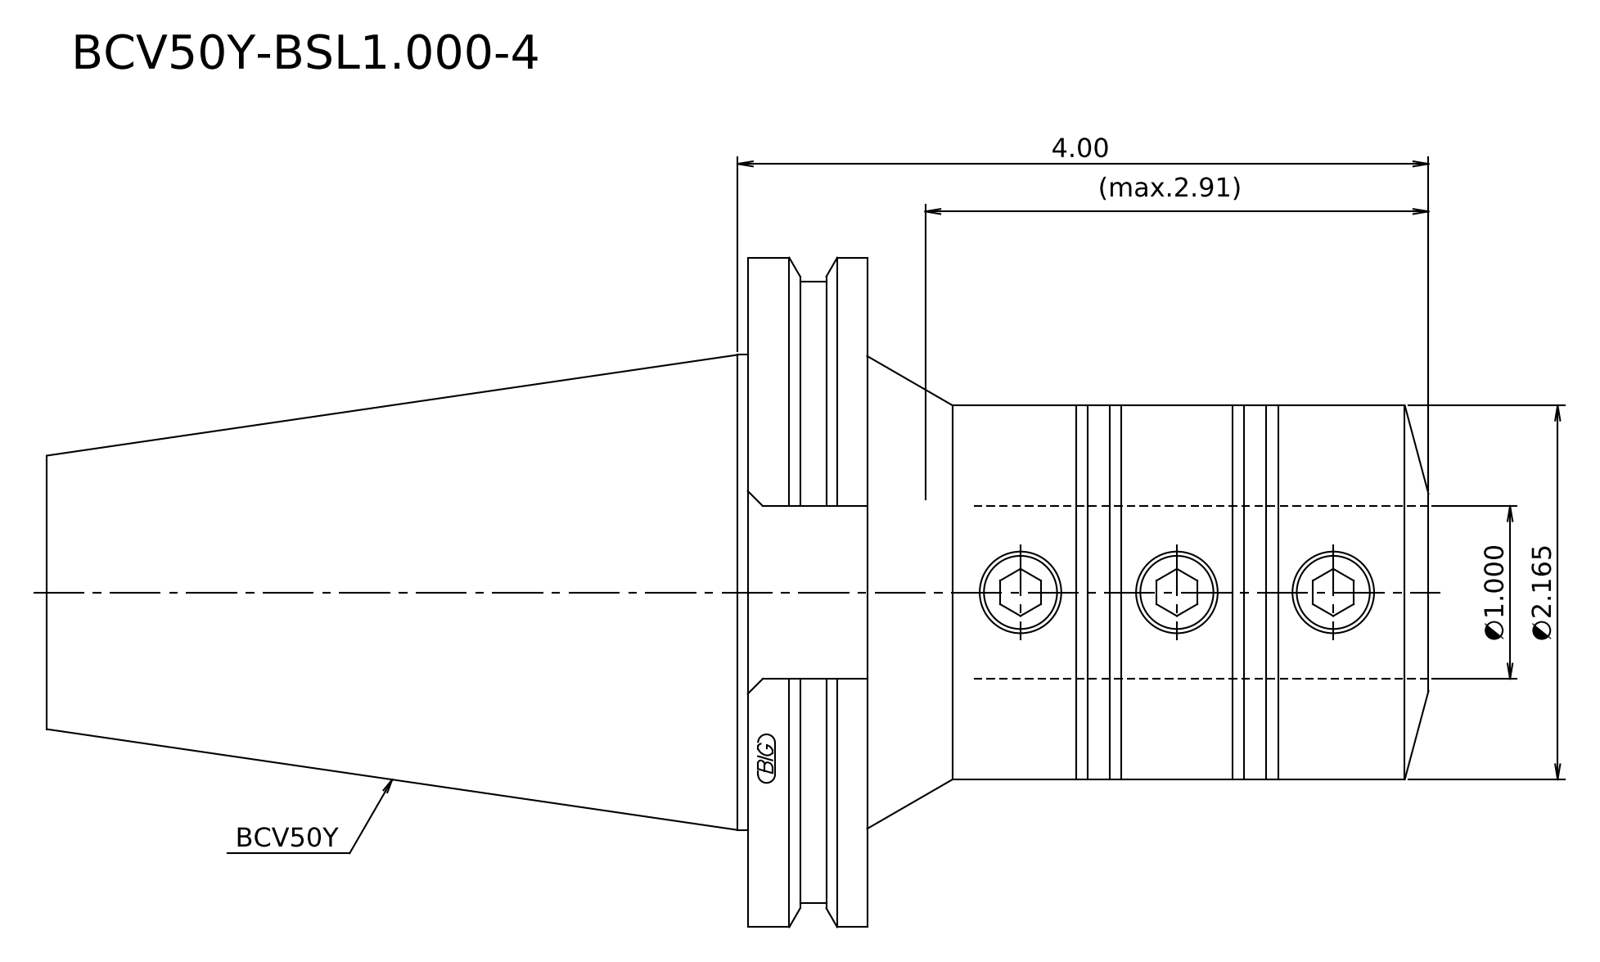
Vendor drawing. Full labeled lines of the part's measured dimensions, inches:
STEP written by: Kubotek KeyCreator 2011 V10.0.2 (22737) (automotive_design)
Units: inches
Bodies: 1 solid, 16 faces (6 planar, 5 cylindrical, 5 other)
Overall size (bounding box): 8 × 3.875 × 3.875
Volume: 35.56 in³ · Surface area: 78.18 in²
Round bosses / shafts (diameter × count): ⌀3.875 ×1, ⌀3.594 ×1, ⌀2.75 ×1, ⌀2.165 ×1
Main face-to-face distances: 0.691, 4.75, 4.059, 3.25, 3.941, 8, 3.487, 0.237, 0.454, 4.513
